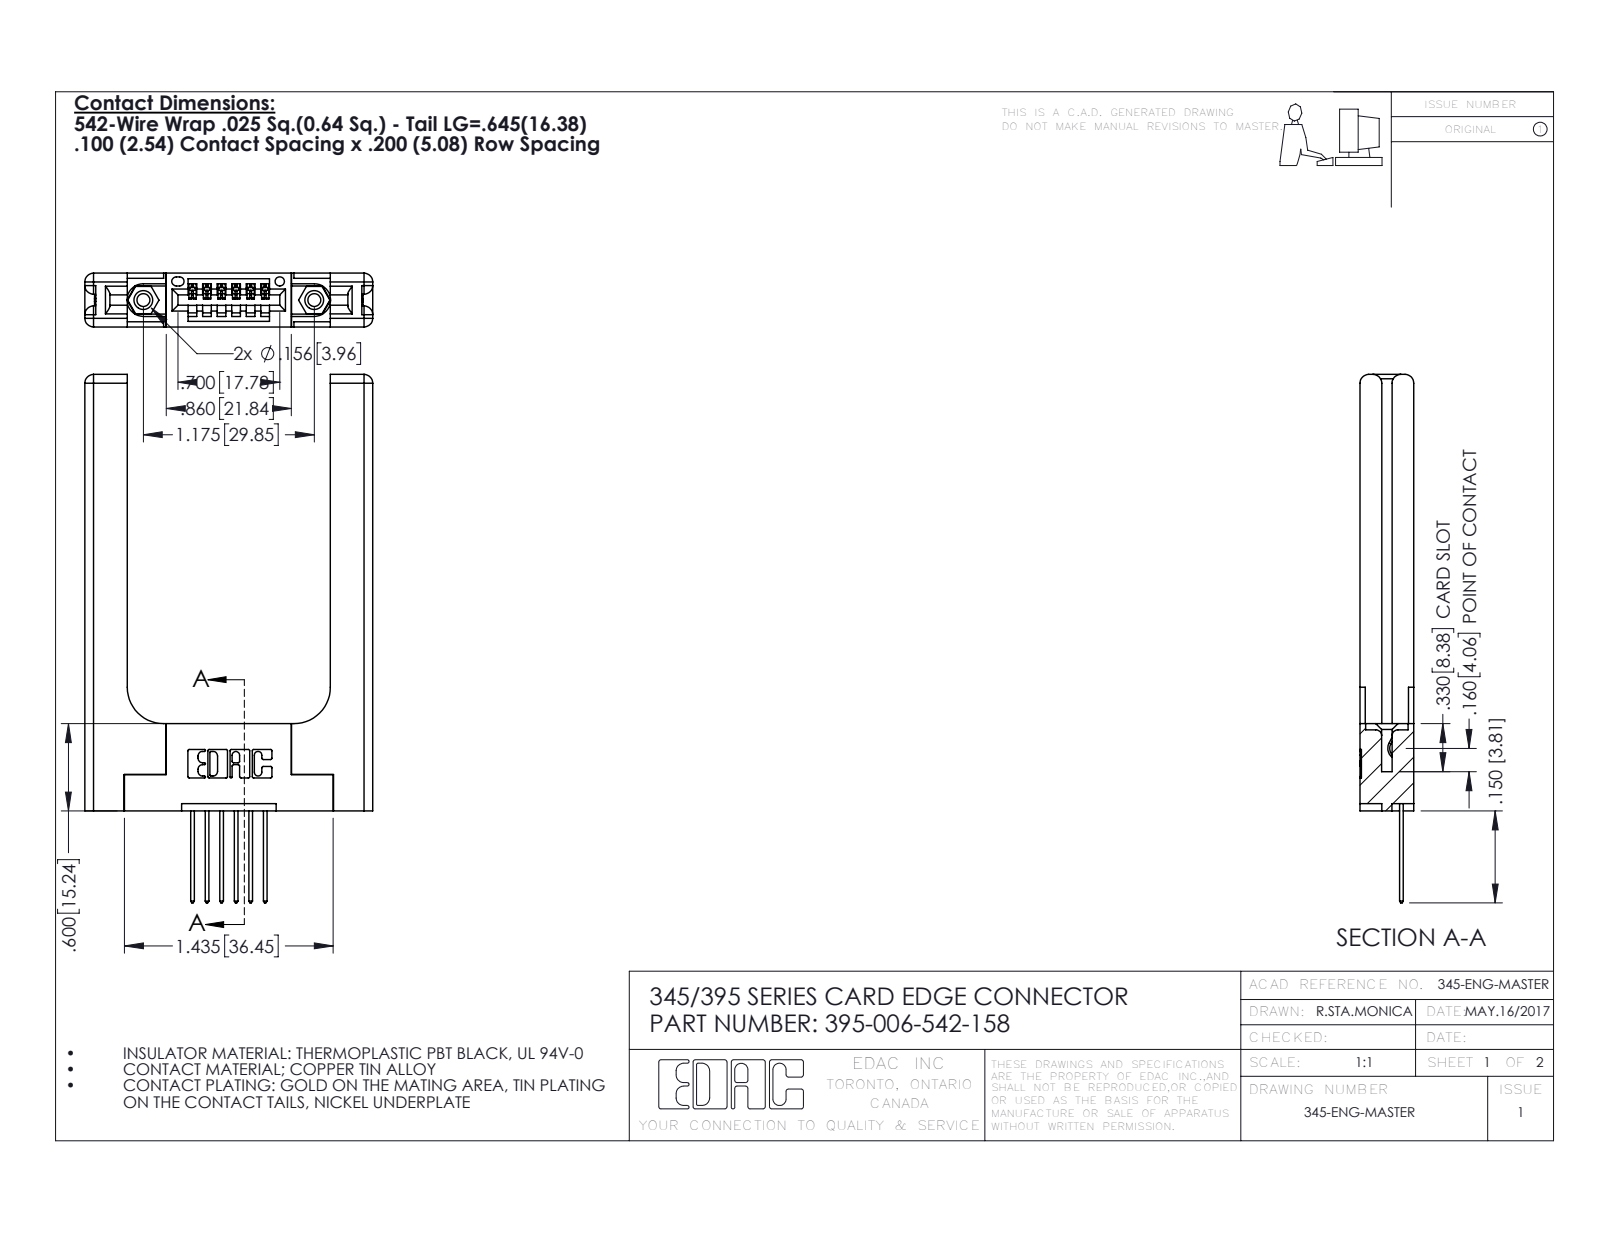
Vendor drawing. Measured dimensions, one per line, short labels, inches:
name: 345-292-001_345-293-142; 345 Part_Flush Mounting Lugs - 0.156 Dia-TH; 395-006-542-158; 345-250-001_345-250-001-102 (+1 more)
written by: SolidWorks 2016 (CONFIG_CONTROL_DESIGN)
unit: in
bodies: 11 solids, 730 faces (468 planar, 202 cylindrical, 60 other)
size: 3.632 × 1.979 × 0.37
volume: 0.793 in³; area: 16.85 in²
holes: 2× ⌀0.089, 2× ⌀0.125, 2× ⌀0.156, 1× ⌀0.064
bosses: 2× ⌀0.155
rounds: 22× R0.01, 16× R0.06, 12× R0.006, 12× R0.01, 6× R0.007, 6× R0.031, 3× R0.026, 2× R0.03
face distances: 0.37, 0.15, 0.22, 0.072, 0.077, 0.148, 1.396, 0.298, 0.071, 0.2
hole spacings: 0.27, 0.946, 1.175
